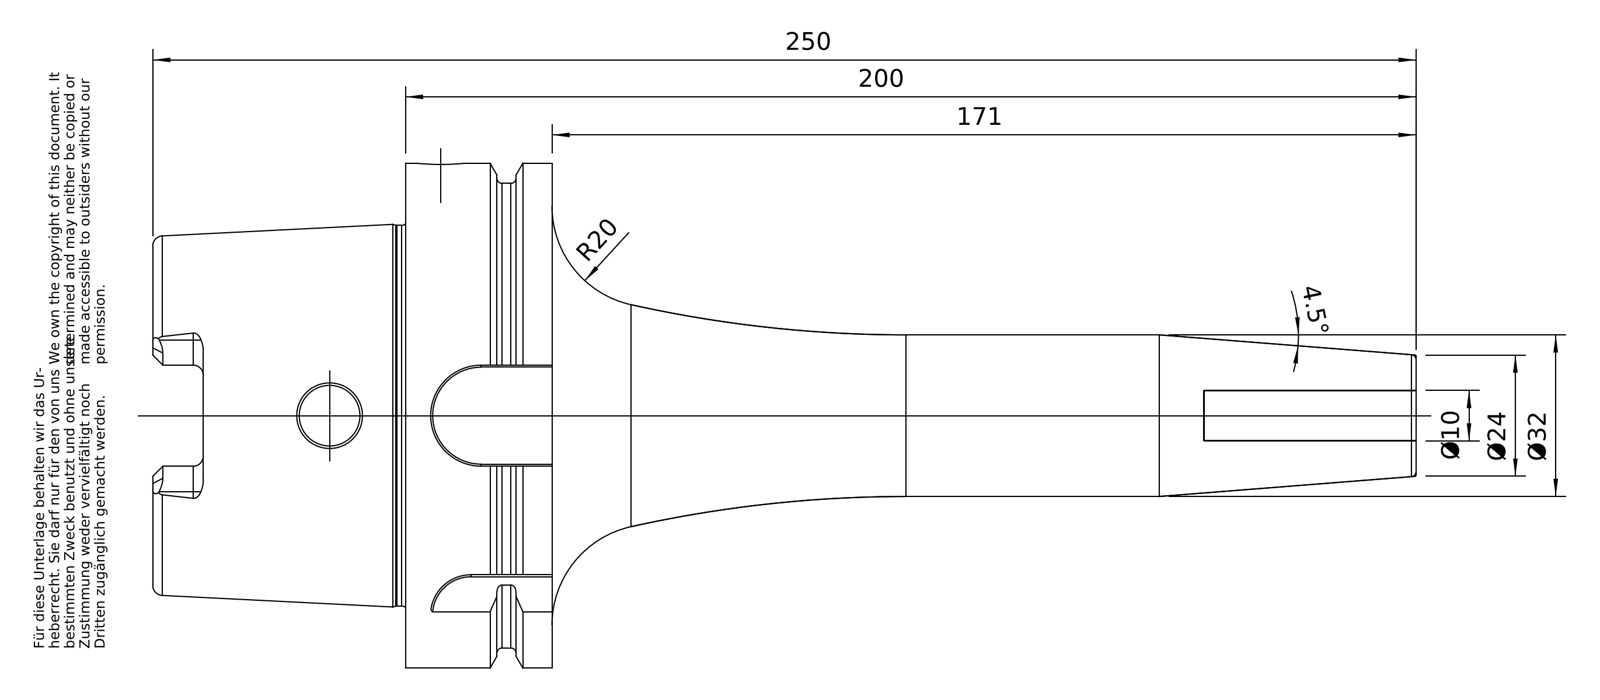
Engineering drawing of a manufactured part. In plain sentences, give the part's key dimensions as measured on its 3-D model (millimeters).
The part is named "A100-146-10". Its 3-D file was written by "PRO/ENGINEER BY PARAMETRIC TECHNOLOGY CORPORATION, 2010430 (CONFIG_CONTROL_DESIGN)". It is 1 solid with 176 faces: 50 planar, 51 cylindrical and 75 other. Overall it measures 250 by 100 by 100 millimeters. Its volume is 415 161 cubic millimeters and its surface area 67 376 square millimeters. Round holes: 2 of diameter 10, 1 of diameter 12, 1 of diameter 22.5, 1 of diameter 24, 1 of diameter 24.32, 1 of diameter 24.5, 1 of diameter 53, 1 of diameter 63. Round bosses or shafts: 1 of diameter 100, 1 of diameter 92, 1 of diameter 75.36, 1 of diameter 32. Partial cylindrical surfaces (rounded edges, fillets, slot ends): 6 of radius 2, 4 of radius 5, 1 of radius 8, 1 of radius 10, 1 of radius 11. The main face-to-face distances are 29, 12.5, 16.5, 50, 62.5, 79, 88, 78.5, 28.5, 16.
